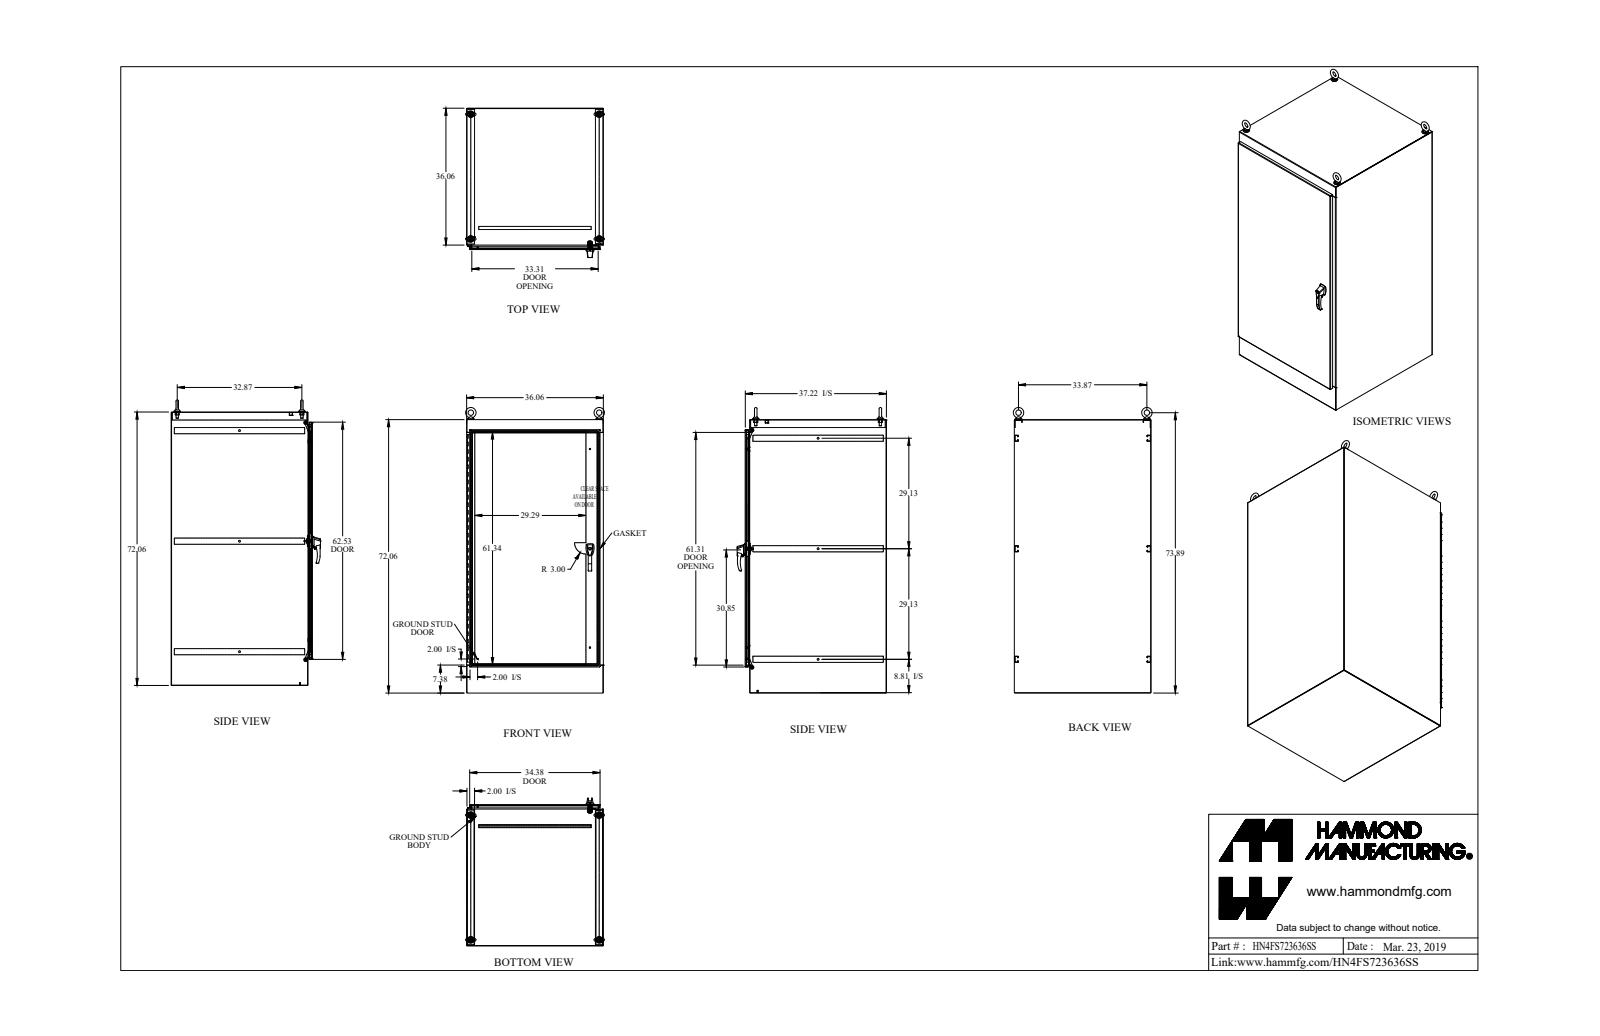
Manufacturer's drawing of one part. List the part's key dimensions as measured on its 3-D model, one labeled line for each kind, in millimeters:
Part name (STEP PRODUCT): HN4FS723636SS
STEP written by: SolidWorks 2018 (AUTOMOTIVE_DESIGN)
Units: millimetres
Bodies: 62 solids, 2004 faces (899 planar, 880 cylindrical, 225 other)
Overall size (bounding box): 1917.4 × 999.8 × 929.7
Volume: 24 170 000 mm³ · Surface area: 19 920 000 mm²
Round holes (diameter × count): ⌀7.7 ×10, ⌀8.9 ×7, ⌀19.1 ×6, ⌀13.4 ×4, ⌀15.9 ×4, ⌀17.3 ×4, ⌀12.7 ×3, ⌀6.4 ×2, ⌀6.5 ×2, ⌀7.1 ×2, ⌀7.1 ×2, ⌀8 ×2
Round bosses / shafts (diameter × count): ⌀44.5 ×4, ⌀38.1 ×4, ⌀31.8 ×4, ⌀18.7 ×4, ⌀25.4 ×2, ⌀19.1 ×2, ⌀16 ×2, ⌀15.9 ×2
Partial cylindrical surfaces — rounded edges, fillets, slot ends (radius × count): R1.1 ×42, R3.5 ×36, R12.7 ×23, R3.2 ×22, R0.5 ×16, R1.5 ×15, R1.2 ×14, R3.6 ×14
Main face-to-face distances: 2.4, 913.5, 943.7, 911.1, 915.9, 1827.9, 941.2, 946.1, 1825.5, 1830.3
Hole centre spacings: 152.4, 304.8, 457.2, 609.6, 762, 860.3, 914.4, 1066.8
